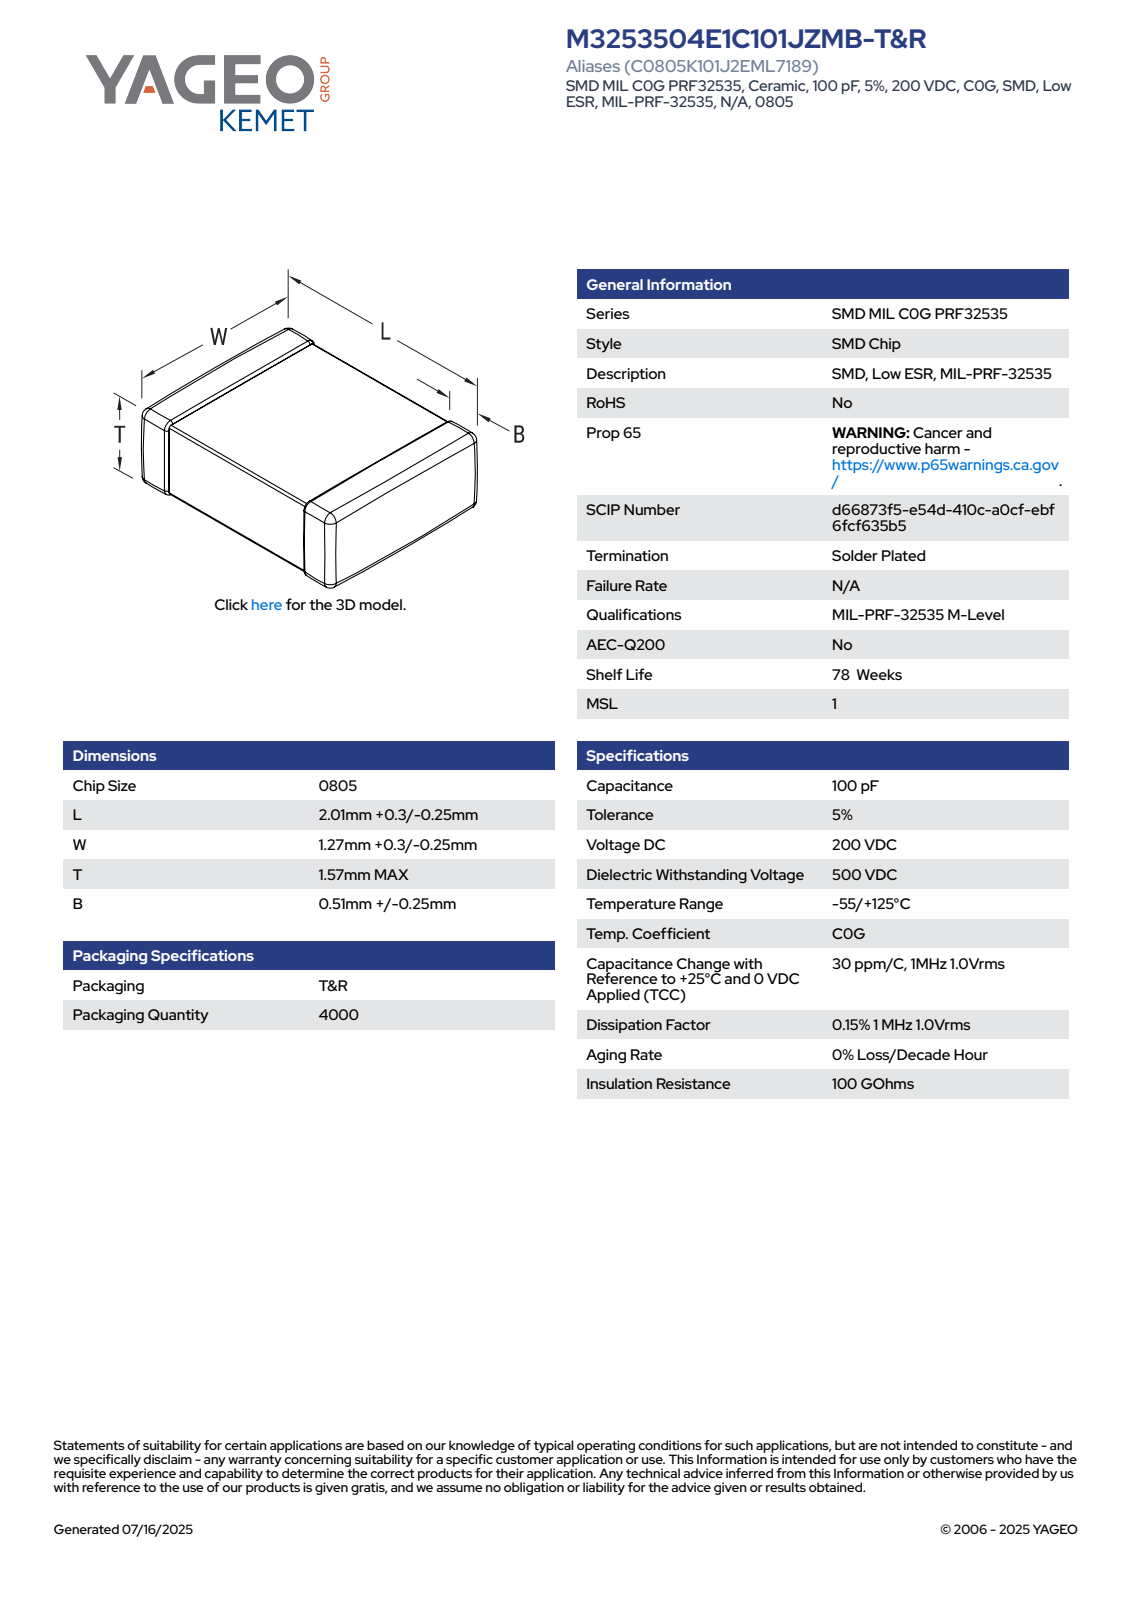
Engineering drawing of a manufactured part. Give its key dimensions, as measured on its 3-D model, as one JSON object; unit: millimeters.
{"part_name": "CCS_STDNOS_0805_L2.31W1.57T1.57B0.51", "step_written_by": "SolidWorks 2021 (AUTOMOTIVE_DESIGN)", "units": "millimeters", "bodies": {"solids": 4, "faces": 121, "planar": 71, "cylindrical": 34, "other": 16}, "overall_size": [2.31, 1.57, 1.57], "volume_mm3": 5, "surface_area_mm2": 19, "face_to_face_distances": [1.54, 1.51, 1.57, 2.31, 0.7, 0.84, 0.73, 0.81, 0.87, 0.67]}
